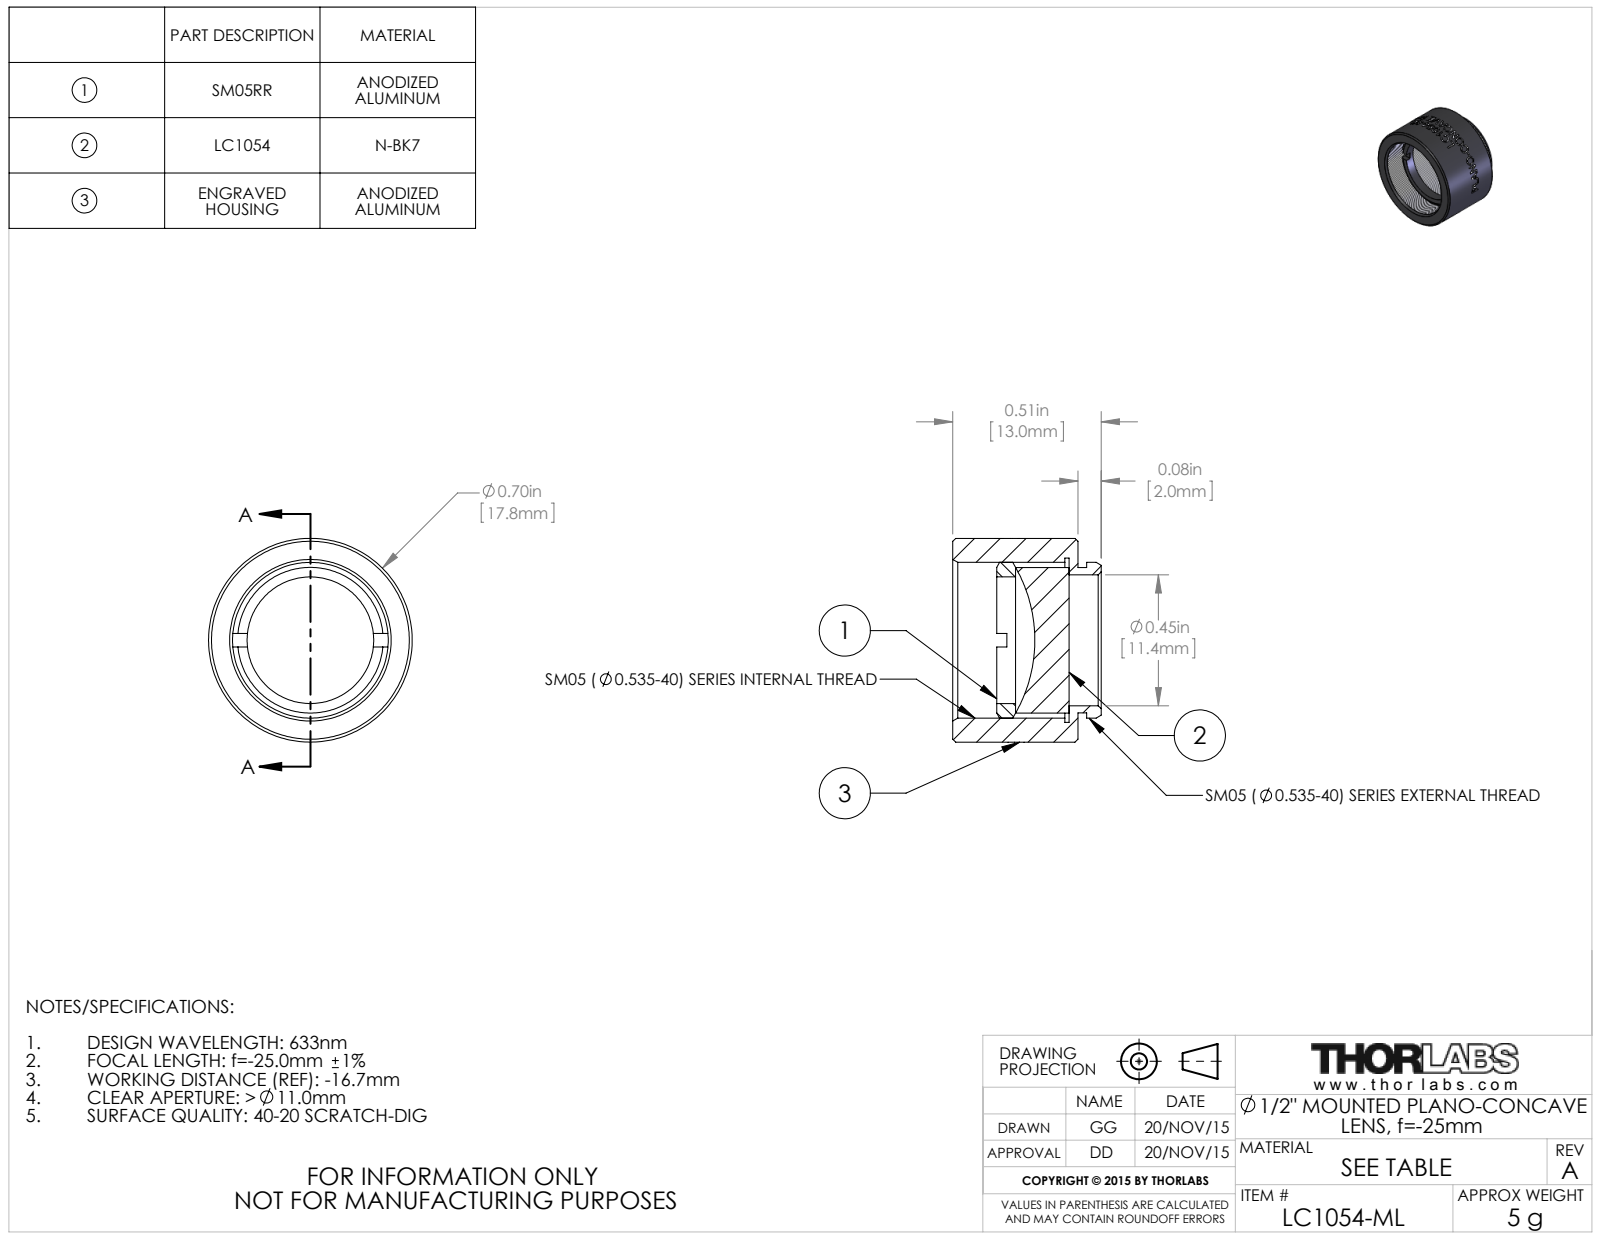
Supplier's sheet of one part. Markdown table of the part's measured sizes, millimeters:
| quantity | value |
| --- | --- |
| part name | TTN045233-E0W |
| STEP written by | SolidWorks 2014 (CONFIG_CONTROL_DESIGN) |
| units | millimeters |
| bodies | 3 solids, 110 faces (16 planar, 77 cylindrical, 17 other) |
| overall size | 17.8 × 17.8 × 13 |
| volume | 1 770 mm³ |
| surface area | 2 214 mm² |
| round holes (diameter × count) | 11 × 1, 11.4 × 1, 13.6 × 1, 14.4 × 1 |
| round bosses / shafts (diameter × count) | 17.8 × 1, 13.6 × 1, 12.7 × 1, 12.7 × 1 |
| main face-to-face distances | 0.8, 10.9, 10.2, 5.4, 4.7, 5.5, 7.1, 6.3, 1.7, 3.8 |
